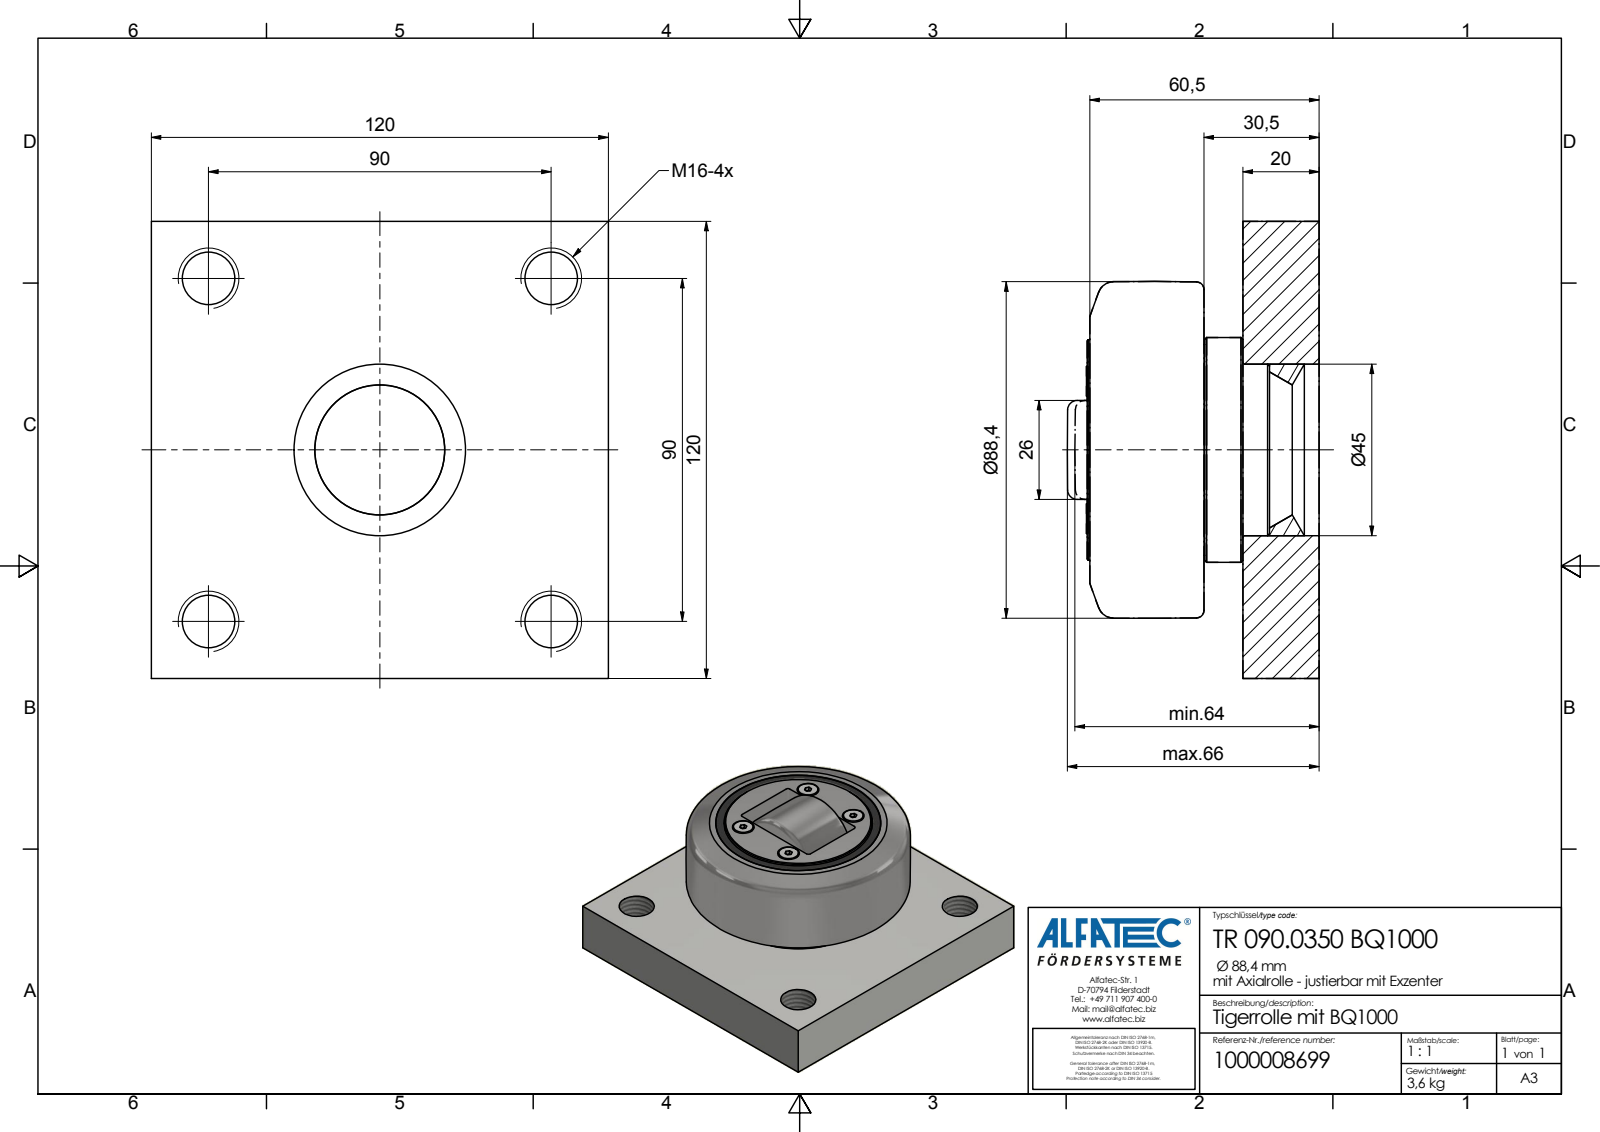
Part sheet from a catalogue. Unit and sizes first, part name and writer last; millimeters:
Units: millimetres
Overall size (bounding box): 120 × 120 × 66.1
Round holes (diameter × count): ⌀13.84 ×4, ⌀45 ×1
Round bosses / shafts (diameter × count): ⌀7.8 ×4, ⌀59 ×1, ⌀57.8 ×1, ⌀55.3 ×1
Partial cylindrical surfaces — rounded edges, fillets, slot ends (radius × count): R1 ×4
Main face-to-face distances: 20, 120, 30.2, 10.2, 30, 60.2, 40.2, 60.9, 40.9, 30.7
Hole centre spacings: 63.64, 90, 127.28
Volume: 476 808 mm³ · Surface area: 58 339 mm²
Bodies: 1 solid, 81 faces (50 planar, 16 cylindrical, 15 other)
Part name (STEP PRODUCT): TR 090.0350 BQ1000_Kontur
STEP written by: Autodesk Inventor 2020 (AP242_MANAGED_MODEL_BASED_3D_ENGINEERING_MIM_LF)
